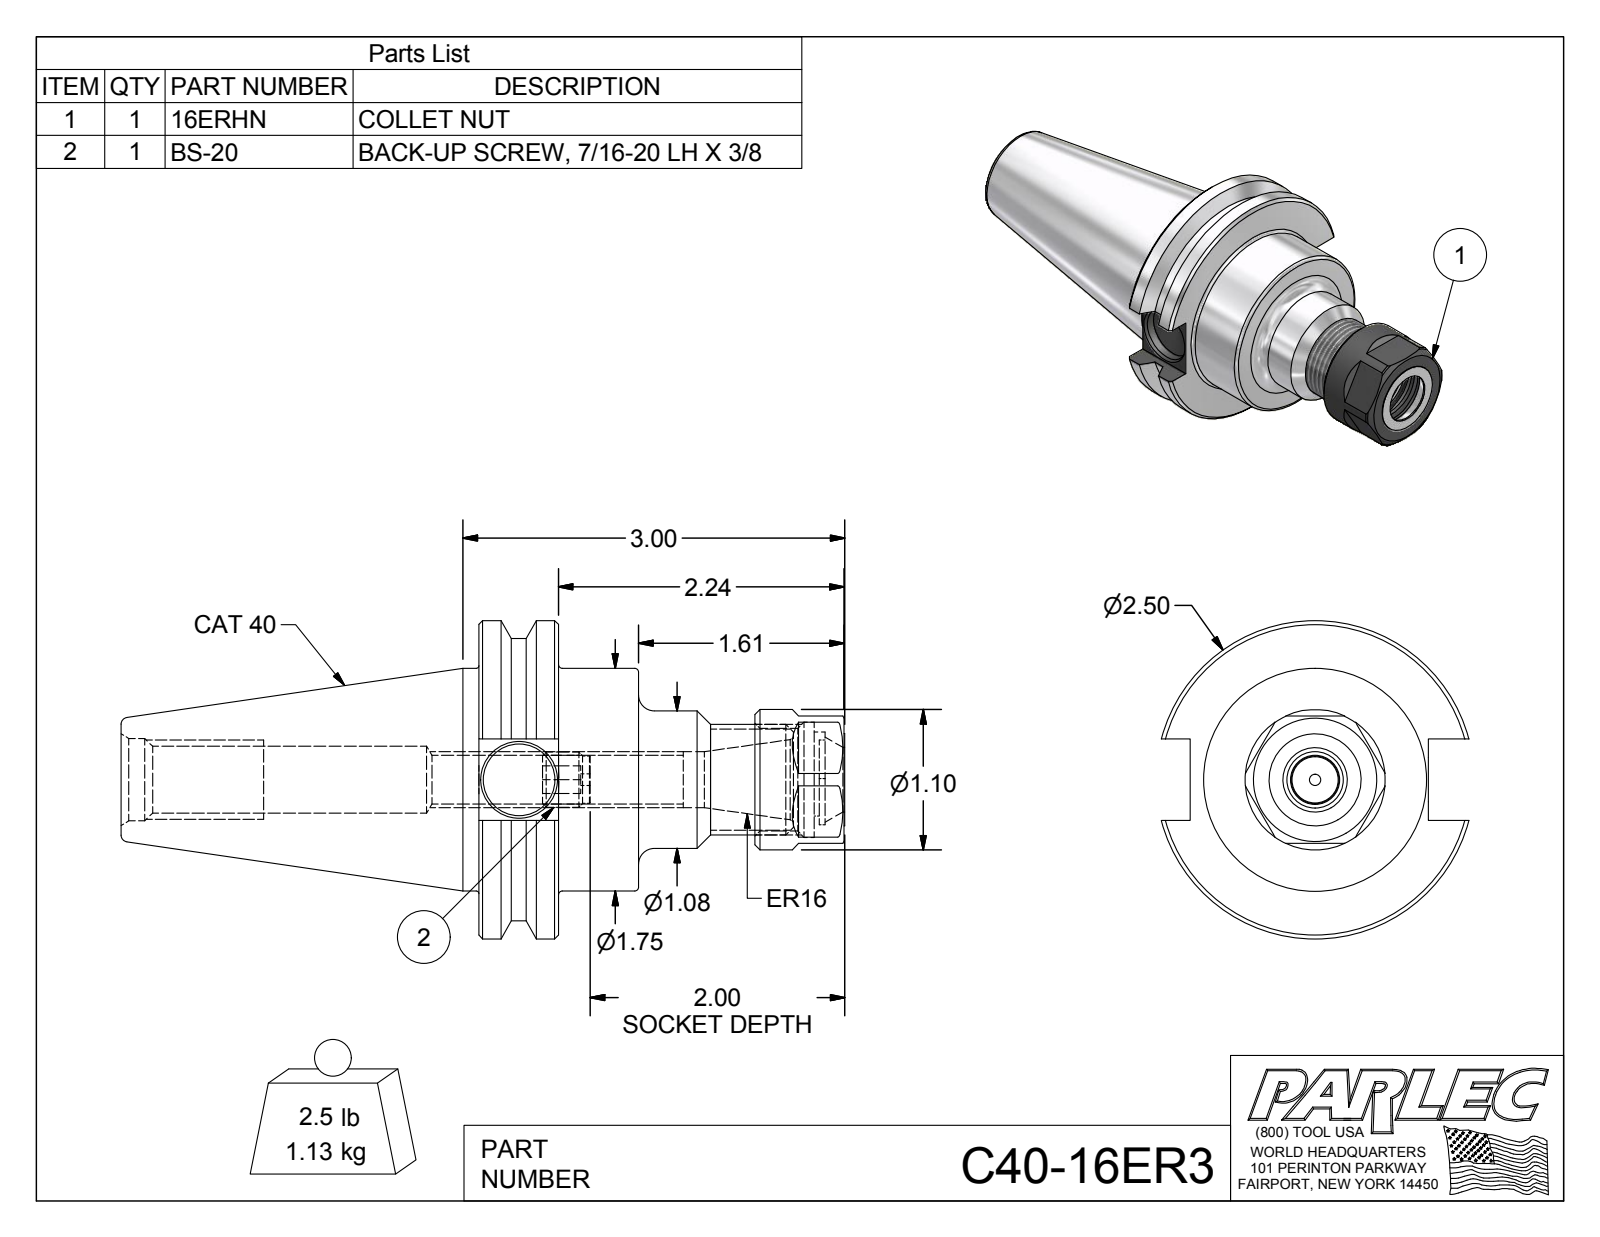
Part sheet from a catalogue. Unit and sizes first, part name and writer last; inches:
Units: inches
Overall size (bounding box): 5.688 × 2.5 × 2.417
Round holes (diameter × count): ⌀0.09 ×1, ⌀0.383 ×1, ⌀0.44 ×1, ⌀0.508 ×1, ⌀0.527 ×1, ⌀0.563 ×1, ⌀0.648 ×1, ⌀0.661 ×1, ⌀0.807 ×1, ⌀0.906 ×1
Round bosses / shafts (diameter × count): ⌀2.5 ×1, ⌀2.219 ×1, ⌀1.75 ×1, ⌀1.102 ×1, ⌀1.08 ×1, ⌀0.866 ×1, ⌀0.724 ×1, ⌀0.432 ×1
Partial cylindrical surfaces — rounded edges, fillets, slot ends (radius × count): R0.354 ×1
Main face-to-face distances: 0.625, 1.255, 0.63, 1, 2.87, 2.245, 1.615, 0.18, 0.82, 2.633
Hole centre spacings: 0.051
Volume: 8.688 in³ · Surface area: 46.18 in²
Bodies: 3 solids, 101 faces (39 planar, 25 cylindrical, 37 other)
Part name (STEP PRODUCT): C40-16ER3; C40-16ER3-1; 16ERHN; BS-20
STEP written by: Autodesk Inventor 2012 (AUTOMOTIVE_DESIGN)
